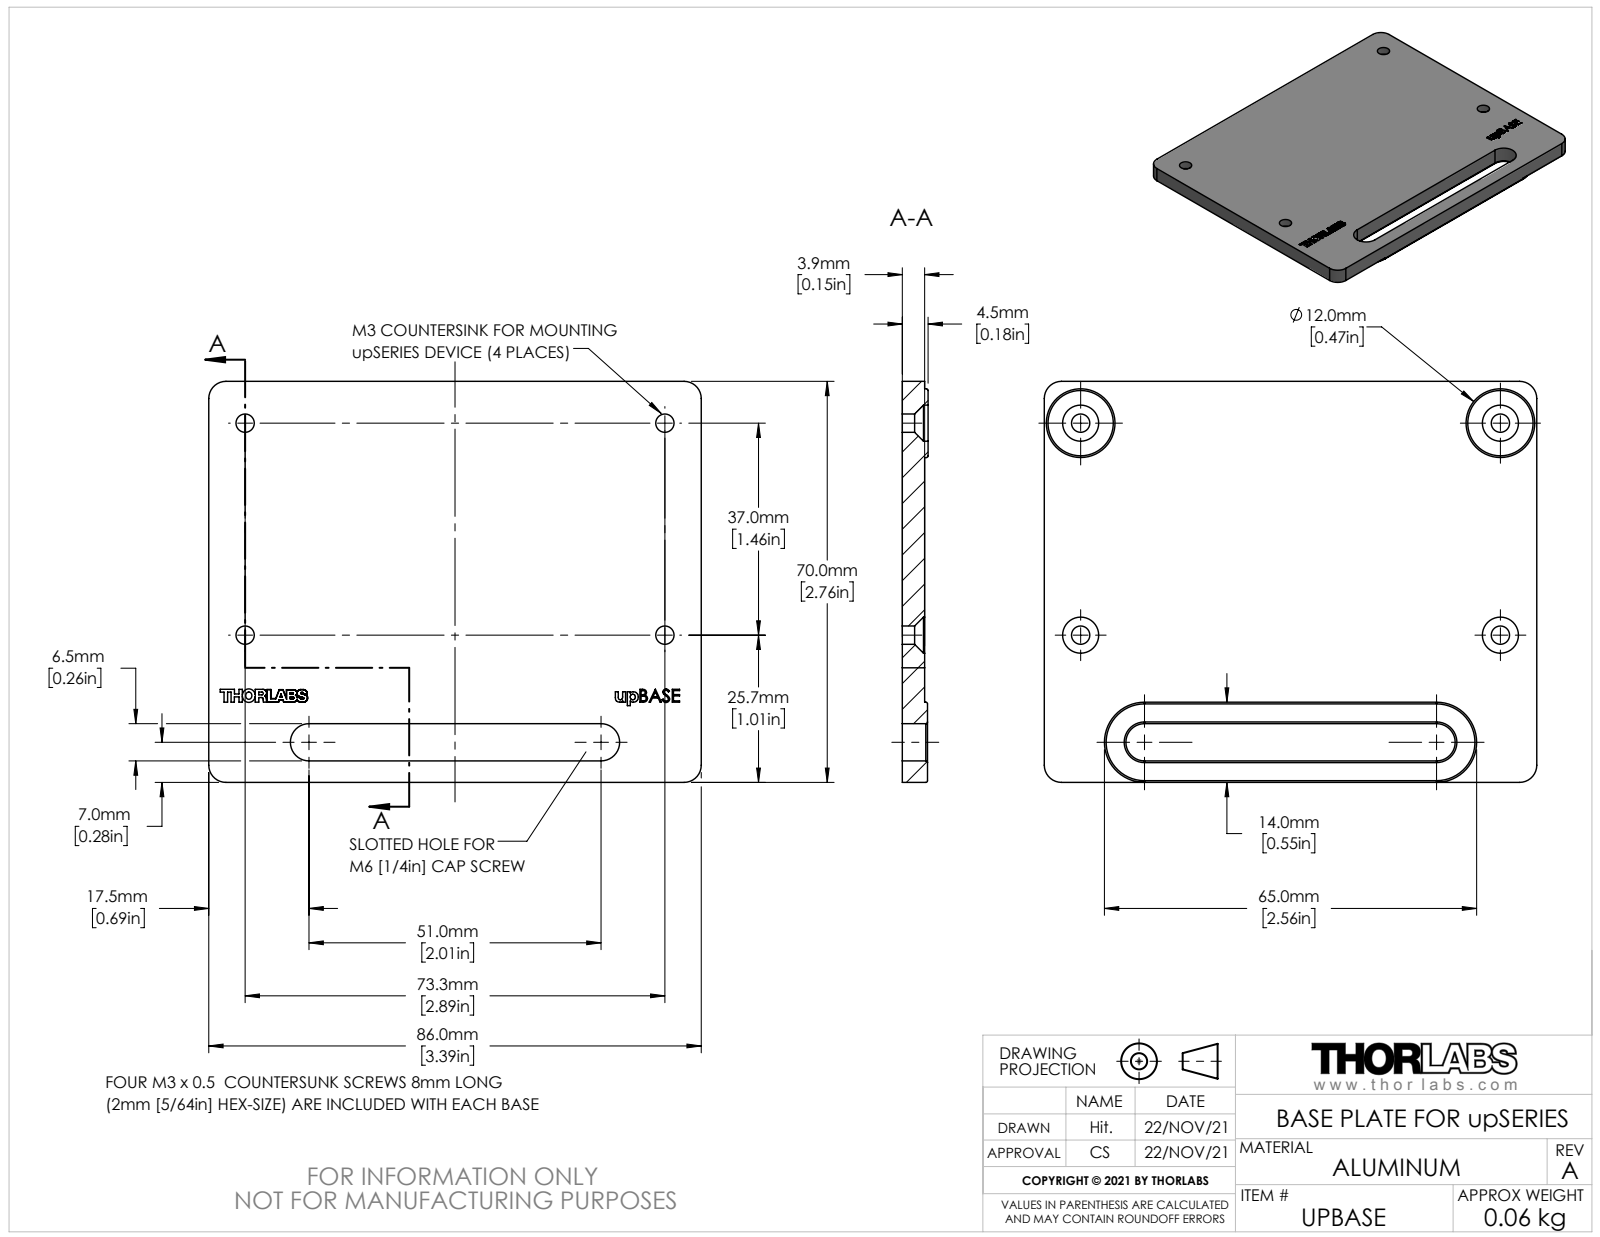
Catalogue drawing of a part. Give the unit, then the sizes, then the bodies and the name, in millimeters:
Units: millimetres
Overall size (bounding box): 86 × 70 × 8.59
Round holes (diameter × count): ⌀3.2 ×4, ⌀6.3 ×4
Round bosses / shafts (diameter × count): ⌀5.35 ×4, ⌀3 ×4, ⌀12 ×2
Partial cylindrical surfaces — rounded edges, fillets, slot ends (radius × count): R0.3 ×4, R3 ×4, R3.25 ×2, R7 ×2
Main face-to-face distances: 3.9, 0.5, 4.4, 70, 86, 3.75, 10.25, 6.5, 66.25, 59.75
Hole centre spacings: 37, 73.3, 82.11
Volume: 22 443 mm³ · Surface area: 13 713 mm²
Bodies: 5 solids, 647 faces (498 planar, 48 cylindrical, 101 other)
Part name (STEP PRODUCT): MTN028059-E0W
STEP written by: SolidWorks 2019 (AUTOMOTIVE_DESIGN)
